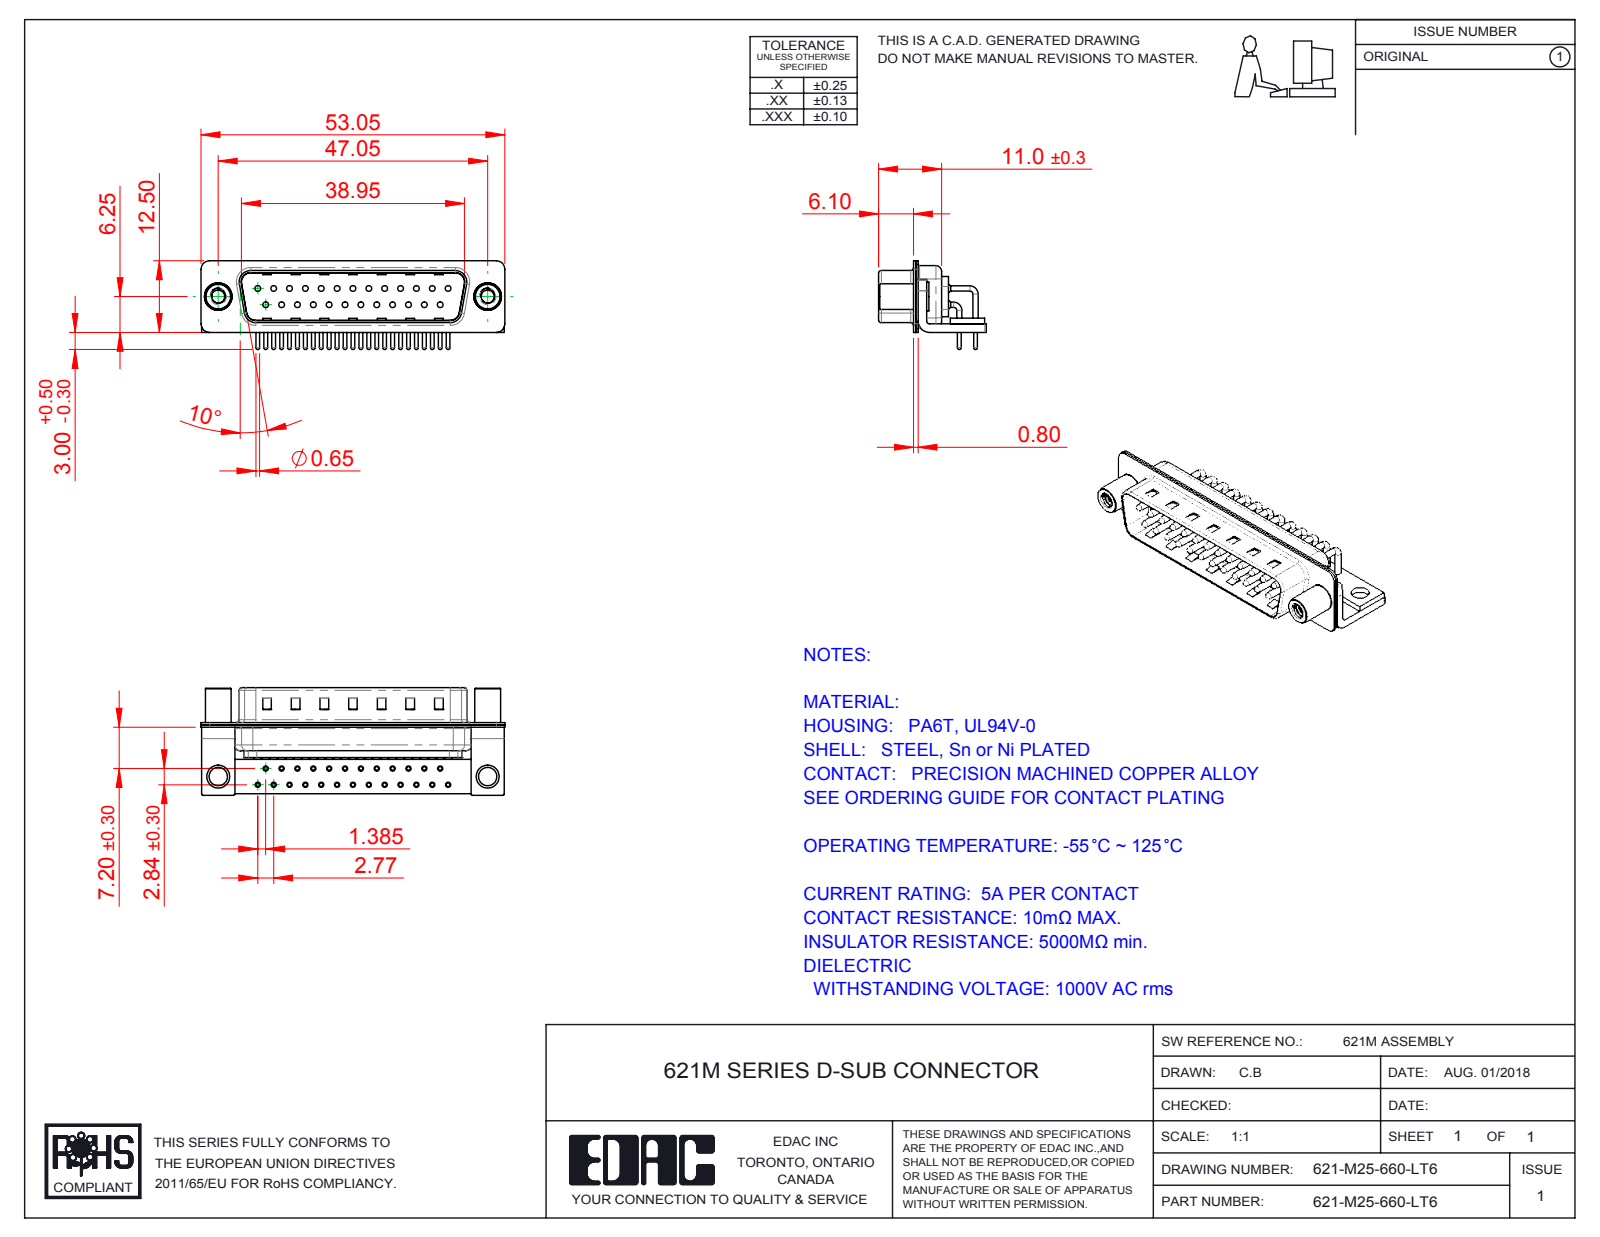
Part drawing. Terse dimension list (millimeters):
name: 621M Contact Row 1; 621-M25-660-LT6; 621M 4-40 Threaded Standoff; 621M Housing_25 Contacts (+5 more)
written by: SolidWorks 2016 (CONFIG_CONTROL_DESIGN)
unit: mm
bodies: 33 solids, 3276 faces (1799 planar, 1151 cylindrical, 326 other)
size: 53.05 × 18.8 × 15.49
volume: 3 511 mm³; area: 9 207 mm²
holes: 25× ⌀0.9, 25× ⌀1, 25× ⌀1.7, 25× ⌀2, 2× ⌀2.26, 2× ⌀3.2, 2× ⌀4, 2× ⌀4.8
bosses: 33× ⌀0.9, 25× ⌀1.5, 25× ⌀0.65, 2× ⌀5, 2× ⌀4.9, 2× ⌀4.5
rounds: 25× R1.01, 16× R0.25, 16× R1.5, 13× R2, 9× R0.5, 8× R1.6, 4× R0.6, 4× R0.65
face distances: 0.4, 0.85, 1.25, 1.5, 9.55, 0.8, 10.4, 8.3, 1, 1.9
hole spacings: 3.16, 2.77, 8.31, 5.54, 11.08, 13.85, 5.04, 16.62
